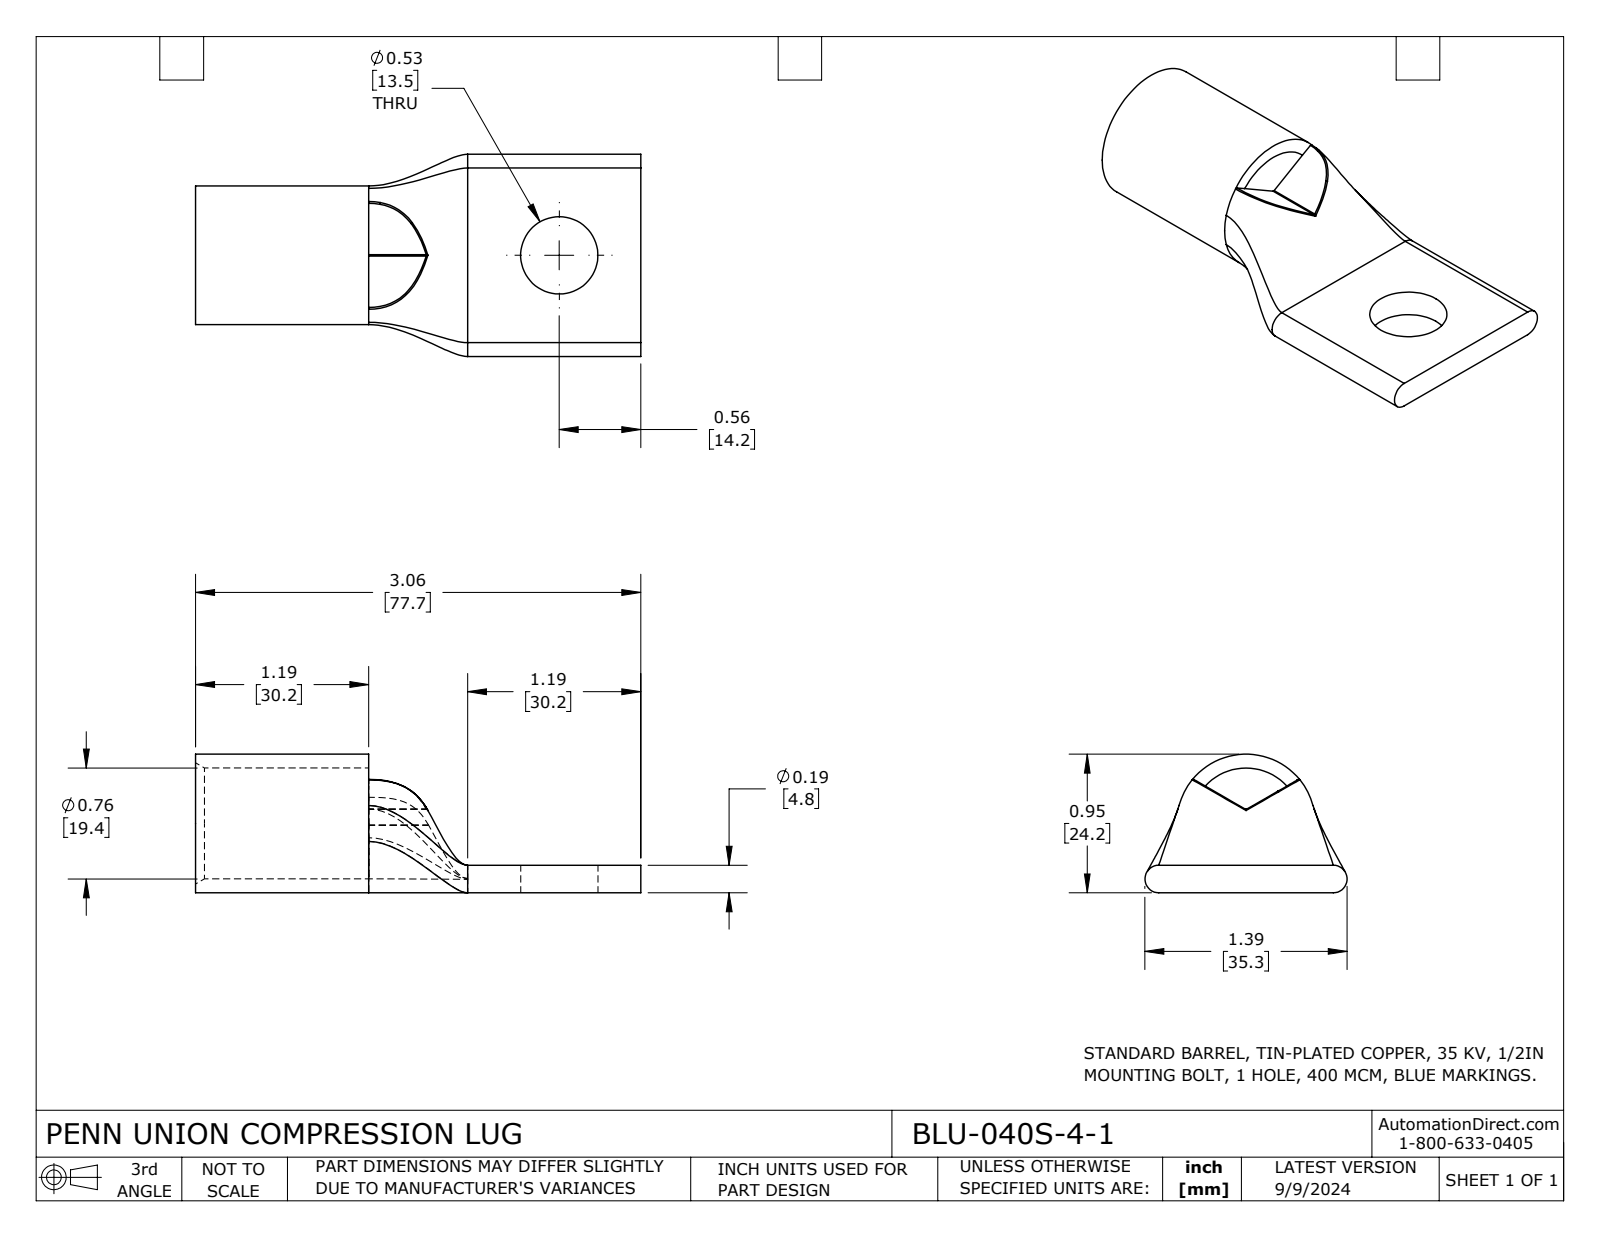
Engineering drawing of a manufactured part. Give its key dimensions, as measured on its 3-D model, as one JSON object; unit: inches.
{"part_name": "BLU-040S-4-1", "step_written_by": "SolidWorks 2023 (CONFIG_CONTROL_DESIGN)", "units": "inches", "bodies": {"solids": 1, "faces": 37, "planar": 11, "cylindrical": 11, "other": 15}, "overall_size": [3.06, 1.39, 0.953], "volume_in3": 0.729, "surface_area_in2": 14.55, "round_holes": [[0.531, 1], [0.762, 1]], "round_bosses_or_shafts": [[0.953, 1]], "partial_cylinders_radius": [[0.01, 2], [0.095, 2]], "face_to_face_distances": [0.19, 0.095, 3.06, 1.19, 1.87, 1.87, 0.68, 1.19]}
